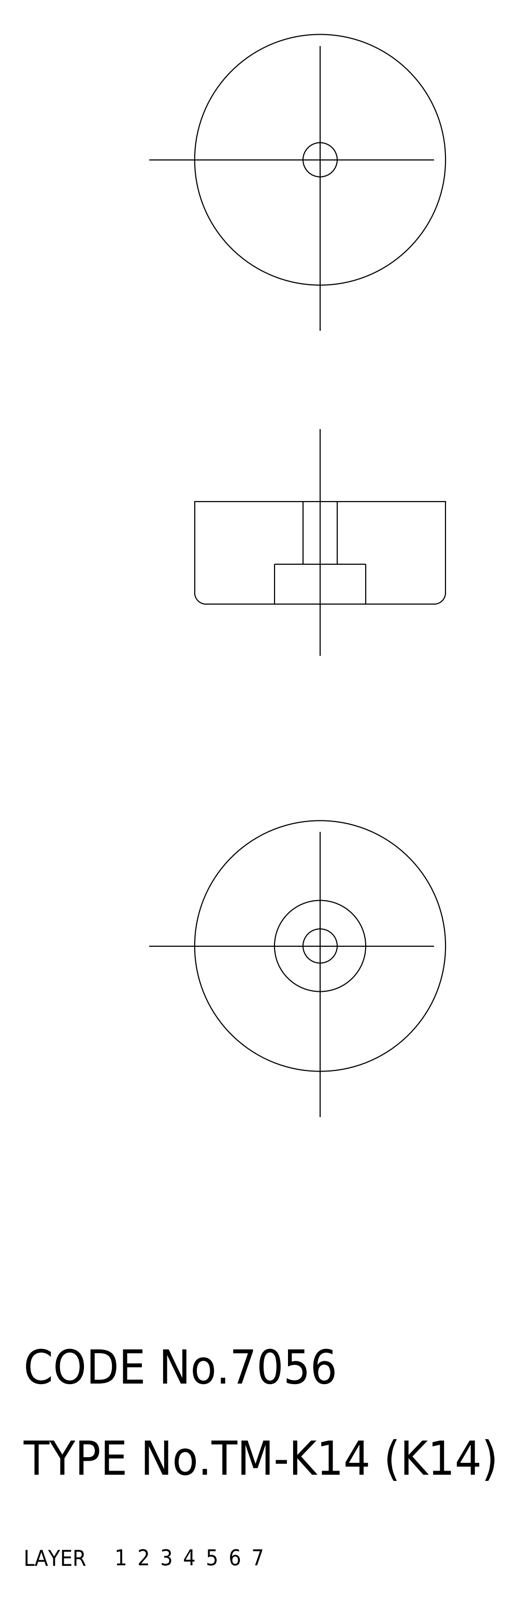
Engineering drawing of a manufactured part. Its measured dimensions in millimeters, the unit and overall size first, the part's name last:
Units: millimetres
Overall size (bounding box): 22 × 22 × 9
Volume: 3 199 mm³ · Surface area: 1 479 mm²
Bodies: 1 solid, 11 faces (0 planar, 0 cylindrical, 11 other)
Part name (STEP PRODUCT): rubber foot
STEP written by: CADfix (AUTOMOTIVE_DESIGN)
